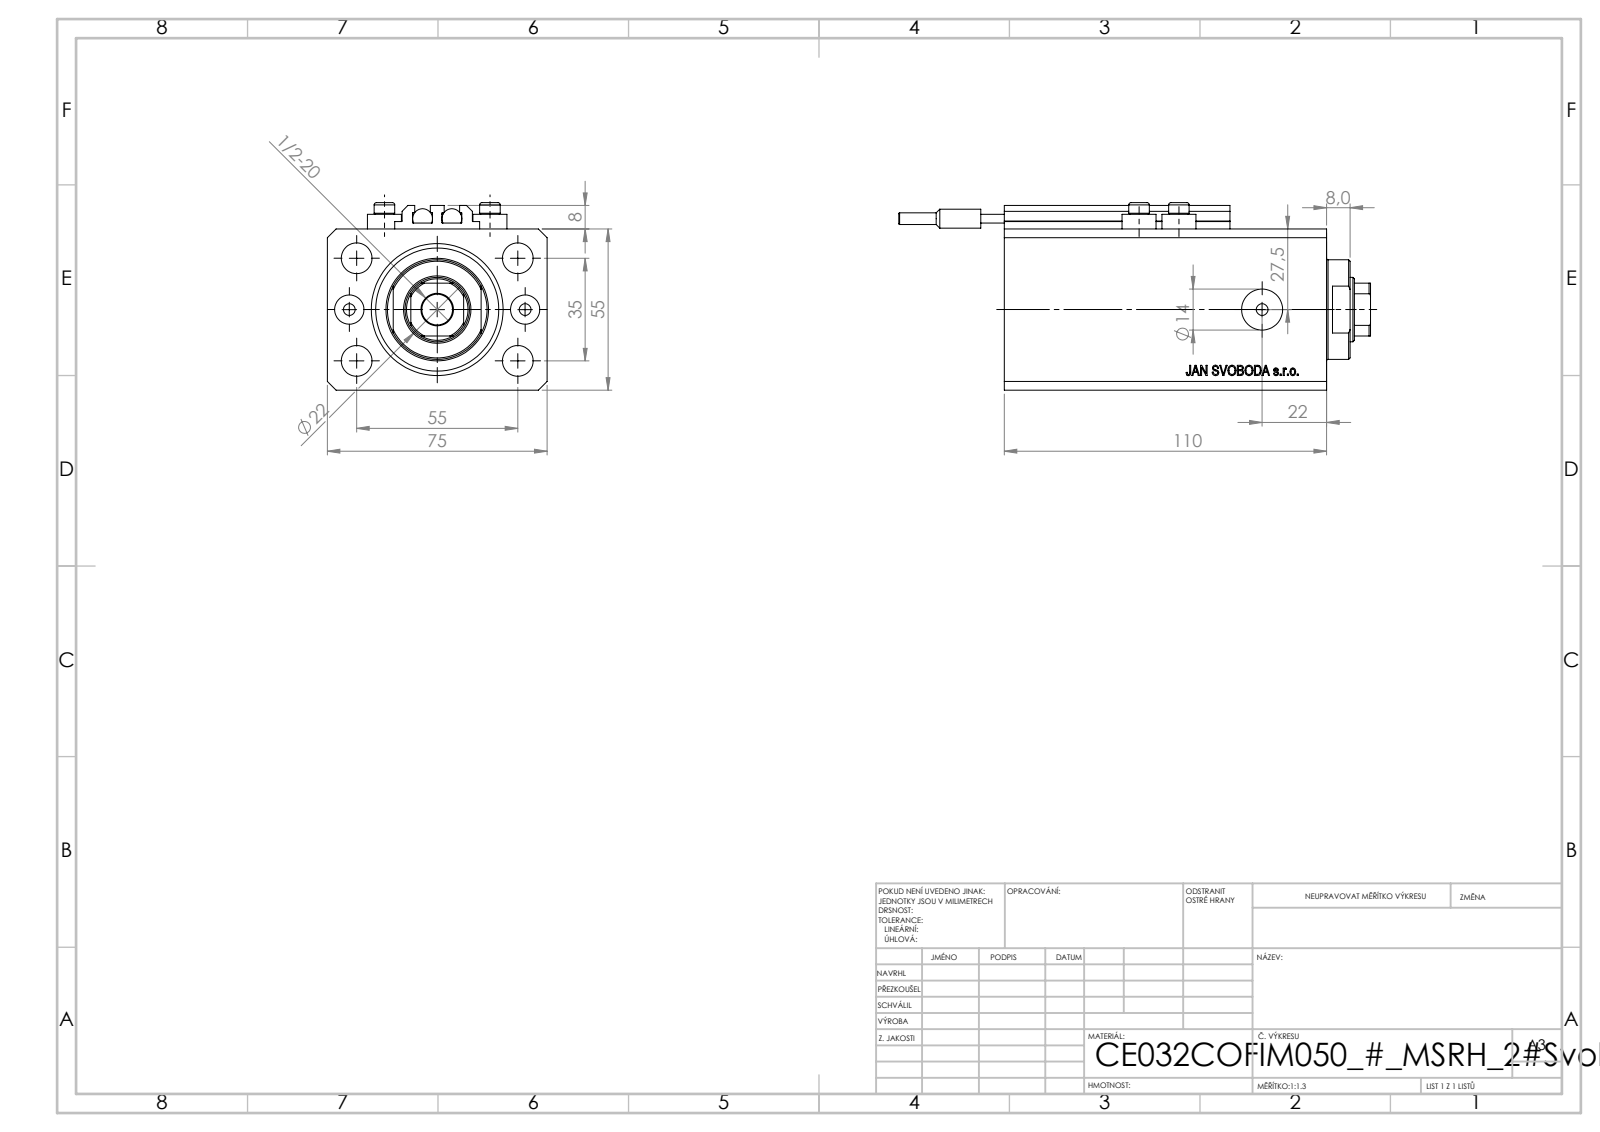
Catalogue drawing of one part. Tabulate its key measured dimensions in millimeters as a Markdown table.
| quantity | value |
| --- | --- |
| part name | V250CE_C_VCP; V250CE_VC_C; V250CE_C_Body; SWITCH_V250CE (+1 more) |
| STEP written by | SolidWorks 2019 (CONFIG_CONTROL_DESIGN) |
| units | millimeters |
| bodies | 10 solids, 1086 faces (536 planar, 98 cylindrical, 452 other) |
| overall size | 161 × 75 × 64 |
| volume | 412 504 mm³ |
| surface area | 93 867 mm² |
| round holes (diameter × count) | 4 × 8, 10.5 × 5, 10 × 2, 14 × 2, 22 × 1, 32 × 1, 45 × 1 |
| round bosses / shafts (diameter × count) | 11.6 × 4, 7 × 4, 6.8 × 2, 6.5 × 2, 4 × 2, 34 × 1 |
| partial cylindrical surfaces (radius × count) | 0.2 × 10, 10.5 × 1 |
| main face-to-face distances | 55, 75, 110, 15, 95, 3, 9.9, 85.1, 100.1, 2 |
| hole center spacings | 17.68, 32.6, 60.1, 13.6, 30, 35, 36, 38.48 |
